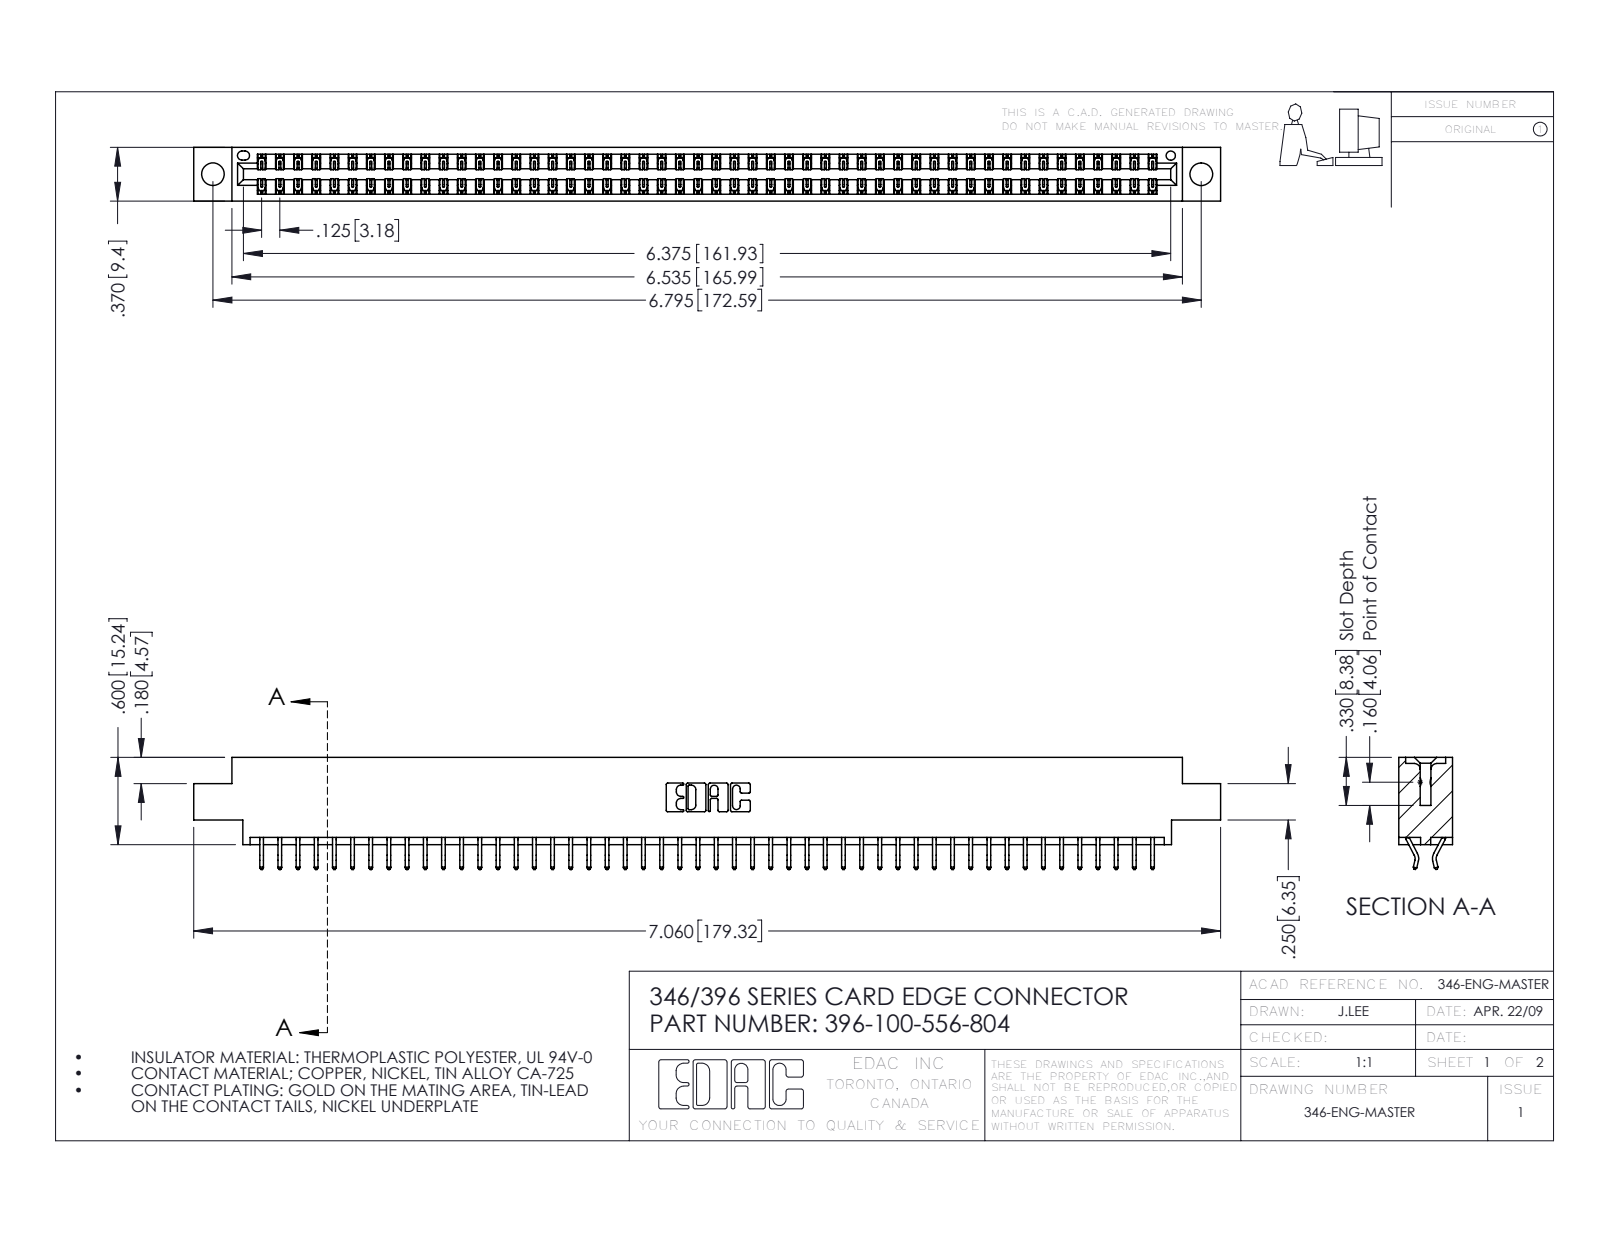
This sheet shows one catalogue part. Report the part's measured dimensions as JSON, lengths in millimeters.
{"part_name": "396-100-556-804; 345-292-001_556 Tail; 346 Part_0.170 Offset - 0.156 Dia-TH", "step_written_by": "SolidWorks 2016 (CONFIG_CONTROL_DESIGN)", "units": "millimeters", "bodies": {"solids": 101, "faces": 5926, "planar": 3980, "cylindrical": 1946, "other": 0}, "overall_size": [179.3, 19.6, 9.4], "volume_mm3": 17300, "surface_area_mm2": 23810, "round_holes": [[4, 2], [1.6, 1]], "partial_cylinders_radius": [[0.2, 150], [0.3, 22], [0.2, 6], [0.8, 6], [0.7, 3], [0.3, 2], [0.4, 2], [0.6, 2]], "face_to_face_distances": [1.2, 8.2, 9.4, 6.4, 0.6, 1.8, 7.6, 7, 3.8, 5.6], "hole_center_spacings": [6.2, 167.3, 172.6]}
